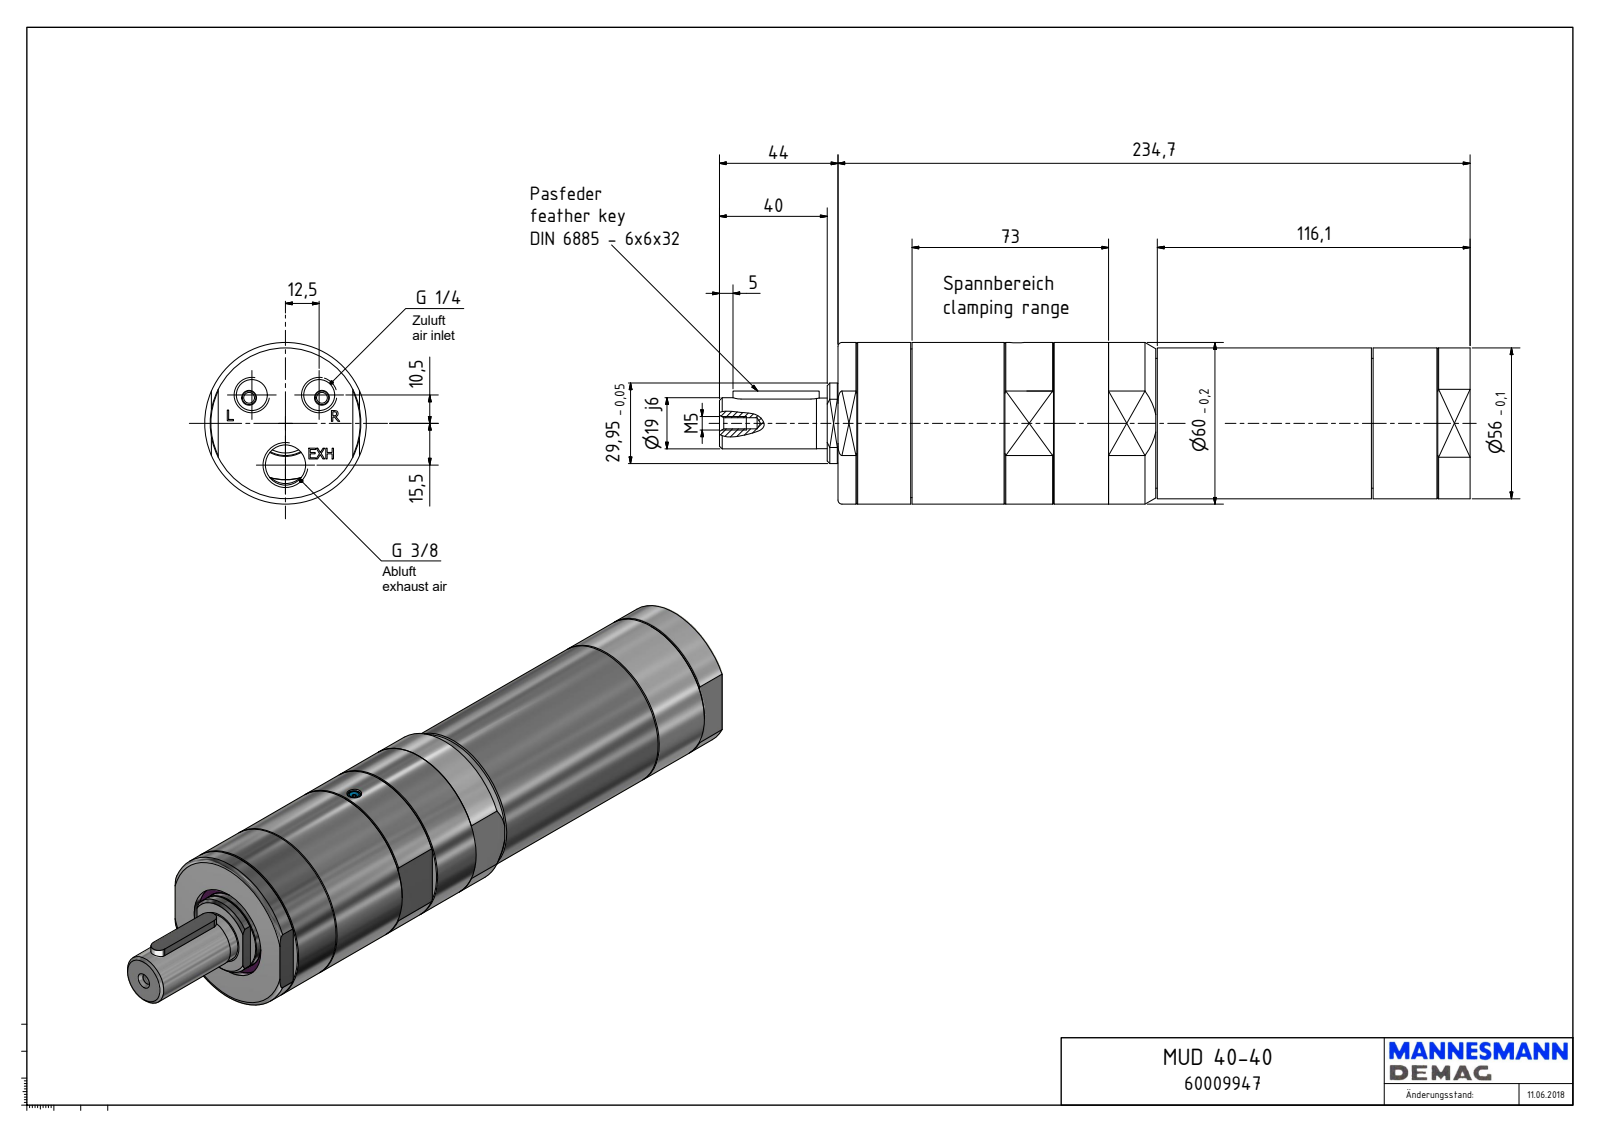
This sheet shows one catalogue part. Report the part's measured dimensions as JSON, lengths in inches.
{"part_name": "MUD 40-40_60009947", "step_written_by": "Autodesk Inventor 2018 (AUTOMOTIVE_DESIGN)", "units": "inches", "bodies": {"solids": 1, "faces": 215, "planar": 115, "cylindrical": 47, "other": 53}, "overall_size": [10.972, 2.362, 2.362], "volume_in3": 38.02, "surface_area_in2": 94.76, "round_holes": [[0.451, 2], [0.061, 1], [0.157, 1], [0.163, 1], [0.217, 1], [0.589, 1], [1.378, 1], [1.437, 1], [1.575, 1], [1.905, 1], [2.18, 1]], "round_bosses_or_shafts": [[2.362, 1], [2.205, 1], [2.172, 1], [1.897, 1], [1.179, 1], [0.748, 1], [0.74, 1], [0.197, 1]], "partial_cylinders_radius": [[0.118, 2], [0.236, 2], [0.748, 1], [0.906, 1], [1.043, 1]], "face_to_face_distances": [9.24, 2.165, 0.024, 3.154, 4.571, 0.098, 2.067, 4.669, 7.799, 3.13], "hole_center_spacings": [0.643, 1.136, 0.61, 0.984]}
